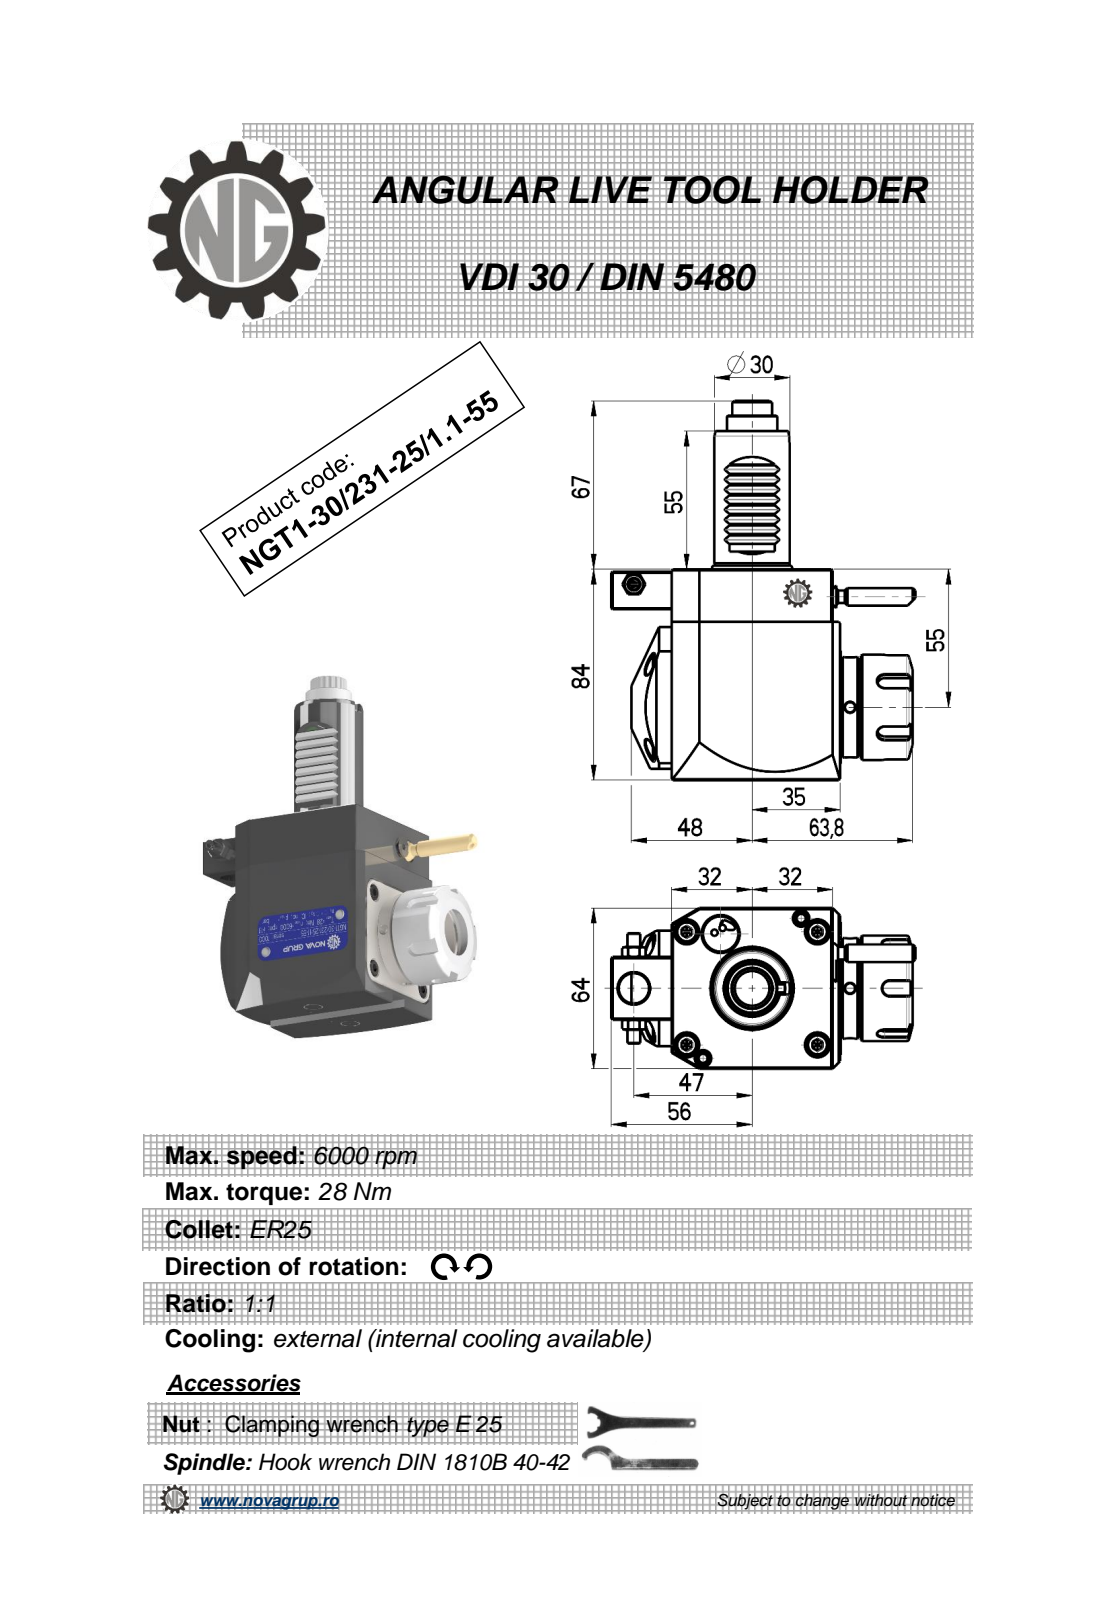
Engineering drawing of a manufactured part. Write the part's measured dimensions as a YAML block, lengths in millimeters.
part_name: "NGT1_30_231_25_1_1_55"
step_written_by: "PRO/ENGINEER BY PARAMETRIC TECHNOLOGY CORPORATION, 2010280 (CONFIG_CONTROL_DESIGN)"
units: millimeters
bodies: {solids: 1, faces: 510, planar: 188, cylindrical: 161, other: 161}
overall_size: [151, 120.88, 65.6]
volume: 455380
surface_area: 47301
round_holes:
  - {diameter: 4, count: 2}
  - {diameter: 2.5, count: 1}
  - {diameter: 3, count: 1}
  - {diameter: 4.2, count: 1}
  - {diameter: 9.5, count: 1}
  - {diameter: 12, count: 1}
  - {diameter: 20.3, count: 1}
round_bosses_or_shafts:
  - {diameter: 8.96, count: 2}
  - {diameter: 5, count: 2}
  - {diameter: 42, count: 1}
  - {diameter: 40, count: 1}
  - {diameter: 33, count: 1}
  - {diameter: 30, count: 1}
  - {diameter: 20, count: 1}
  - {diameter: 7, count: 1}
partial_cylinders:
  - {radius: 1.98, count: 36}
  - {radius: 0.26, count: 12}
  - {radius: 0.3, count: 8}
  - {radius: 3, count: 5}
  - {radius: 3.5, count: 4}
  - {radius: 160, count: 2}
  - {radius: 7.08, count: 1}
  - {radius: 7.92, count: 1}
face_to_face_distances: [64, 84, 67.2, 67, 3.2, 3, 83, 80, 0.5, 55]
hole_center_spacings: [14.22, 46.17, 46.5, 85.95, 98.94]
